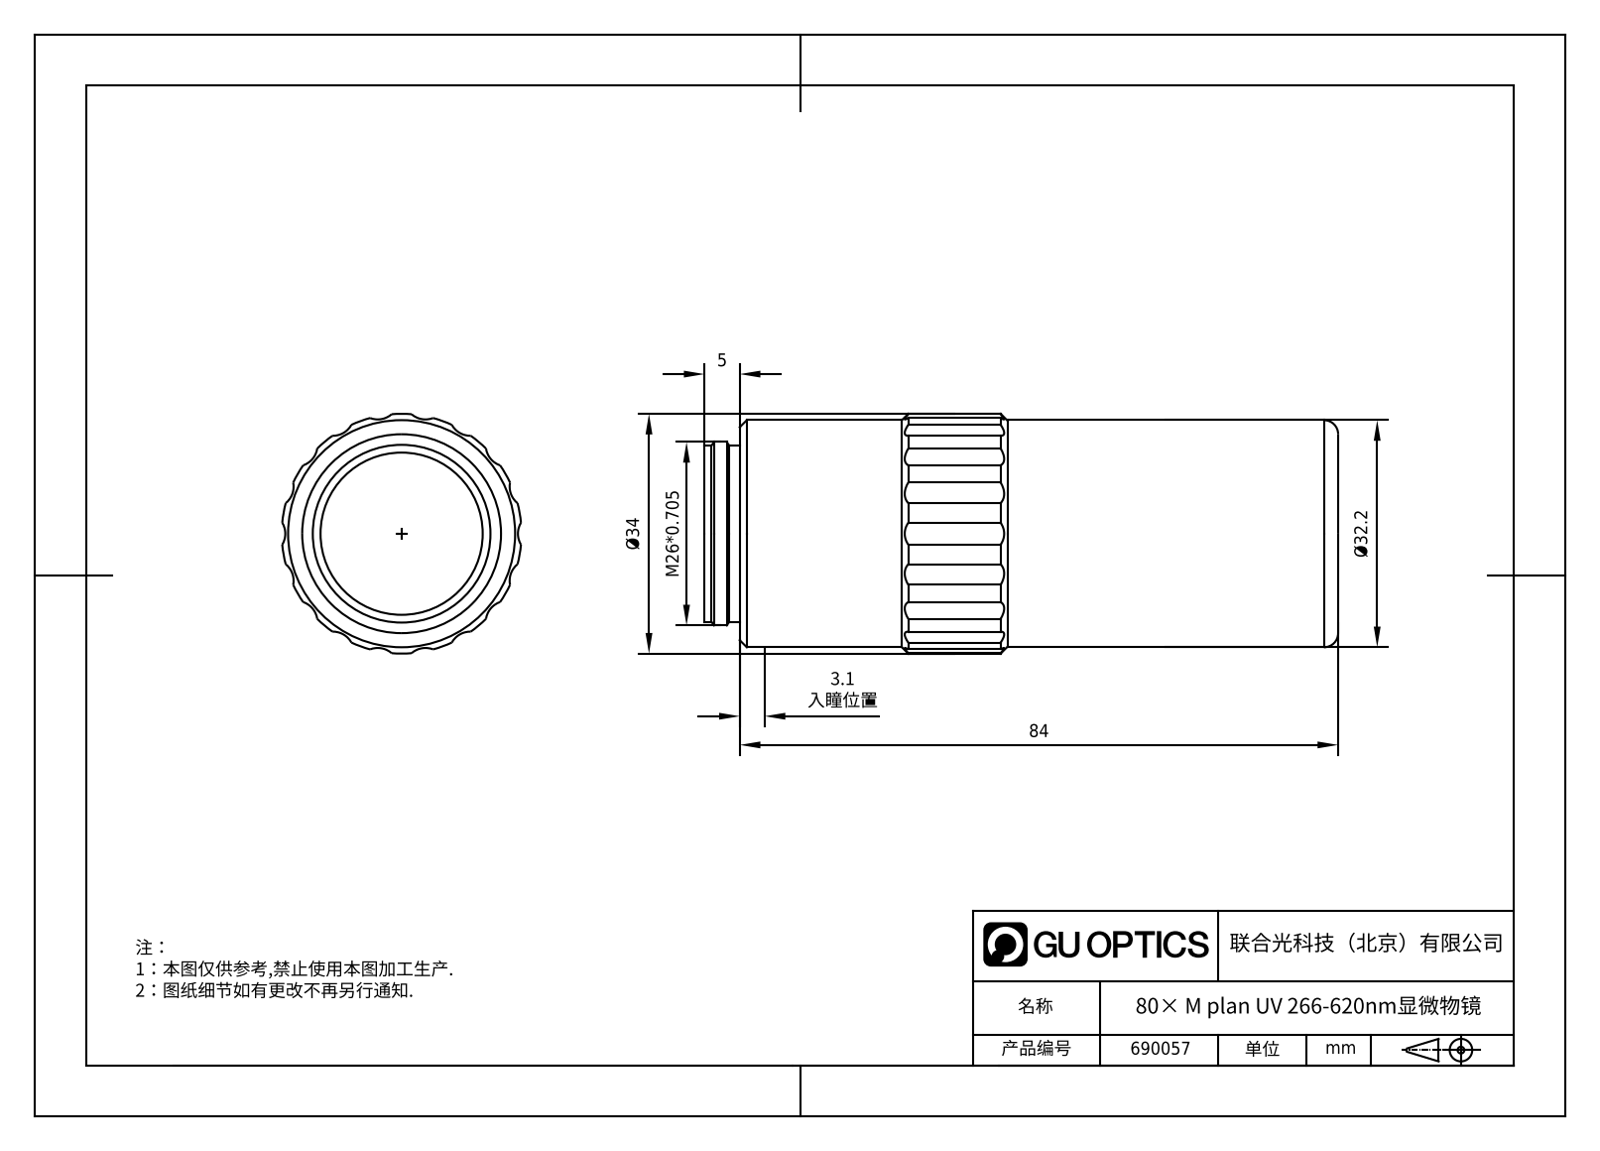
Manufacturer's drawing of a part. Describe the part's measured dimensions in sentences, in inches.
The part is named "690057". Its 3-D file was written by "SolidWorks 2020 (CONFIG_CONTROL_DESIGN)". It is 1 solid with 55 faces: 6 planar, 43 cylindrical and 6 other. Overall it measures 3.543 by 1.339 by 1.333 inches. Its volume is 4.425 cubic inches and its surface area 16.69 square inches. Round holes: 1 of diameter 0.157, 1 of diameter 0.551. Round bosses or shafts: 1 of diameter 1.268, 1 of diameter 1.024, 1 of diameter 0.984. Partial cylindrical surfaces (rounded edges, fillets, slot ends): 18 of radius 0.118, 1 of radius 0.669. The main face-to-face distances are 3.543, 0.197, 3.346, 0.039, 3.504, 3.307, 0.157, 3.465, 1.693, 1.654.
